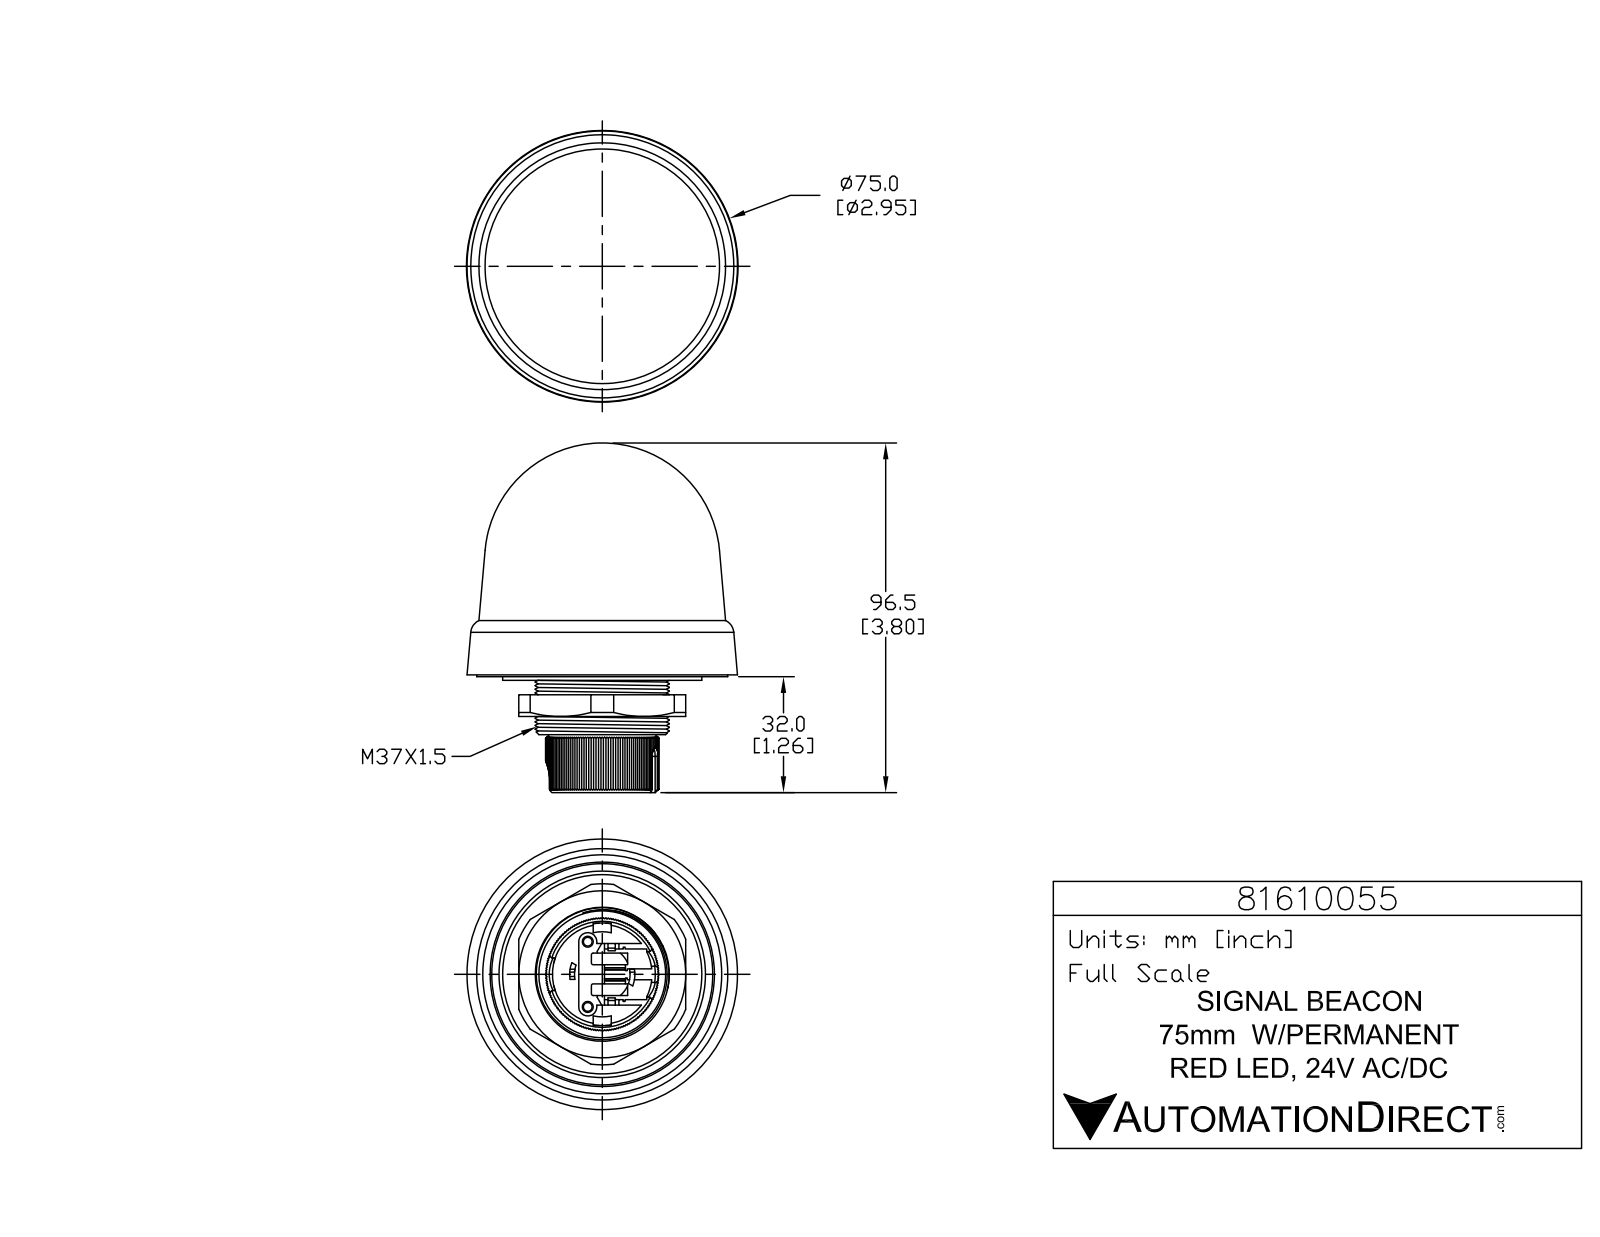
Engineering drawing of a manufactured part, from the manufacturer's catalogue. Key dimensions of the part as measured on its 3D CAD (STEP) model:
Part name (STEP PRODUCT): 81610055
STEP written by: SolidWorks 2019 (CONFIG_CONTROL_DESIGN)
Units: inches
Bodies: 3 solids, 560 faces (432 planar, 80 cylindrical, 48 other)
Overall size (bounding box): 3.799 × 2.941 × 2.941
Volume: 12.36 in³ · Surface area: 58.68 in²
Round holes (diameter × count): ⌀0.094 ×2, ⌀0.118 ×2, ⌀0.604 ×1, ⌀1.142 ×1
Round bosses / shafts (diameter × count): ⌀0.217 ×2, ⌀0.067 ×2, ⌀2.165 ×1, ⌀1.457 ×1, ⌀0.925 ×1
Partial cylindrical surfaces — rounded edges, fillets, slot ends (radius × count): R0.008 ×6, R0.039 ×6, R0.02 ×4, R0.031 ×2, R0.079 ×2, R0.098 ×2, R0.177 ×1, R0.354 ×1
Main face-to-face distances: 0.177, 0.354, 0.197, 0.433, 0.512, 0.335, 0.059, 0.394, 0.118, 0.157
Hole centre spacings: 0.388, 0.709
